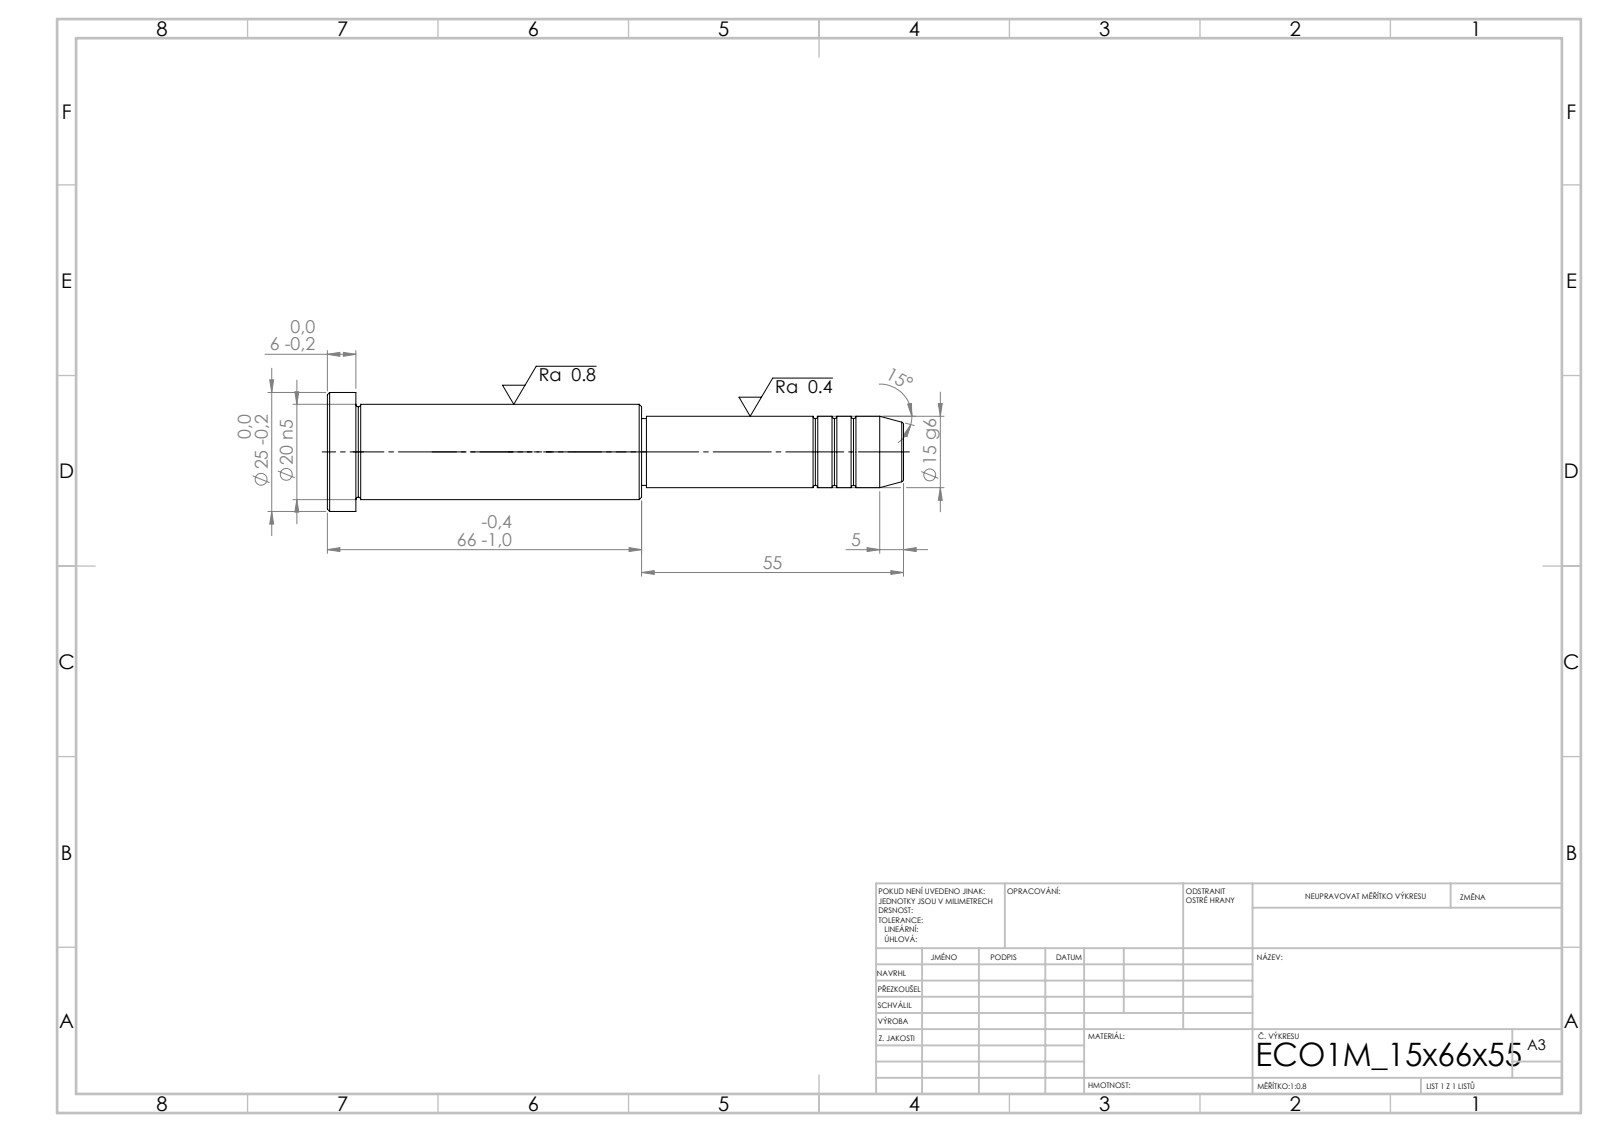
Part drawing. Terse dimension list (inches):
written by: SolidWorks 2019 (CONFIG_CONTROL_DESIGN)
unit: in
bodies: 1 solid, 43 faces (5 planar, 14 cylindrical, 24 other)
size: 4.764 × 0.984 × 0.984
volume: 1.907 in³; area: 12.16 in²
bosses: 1× ⌀0.984, 1× ⌀0.787, 1× ⌀0.591, 1× ⌀0.551
face distances: 0.236, 2.362, 2.598, 2.165, 4.528, 4.764, 2.126, 0.039, 2.402, 2.638
